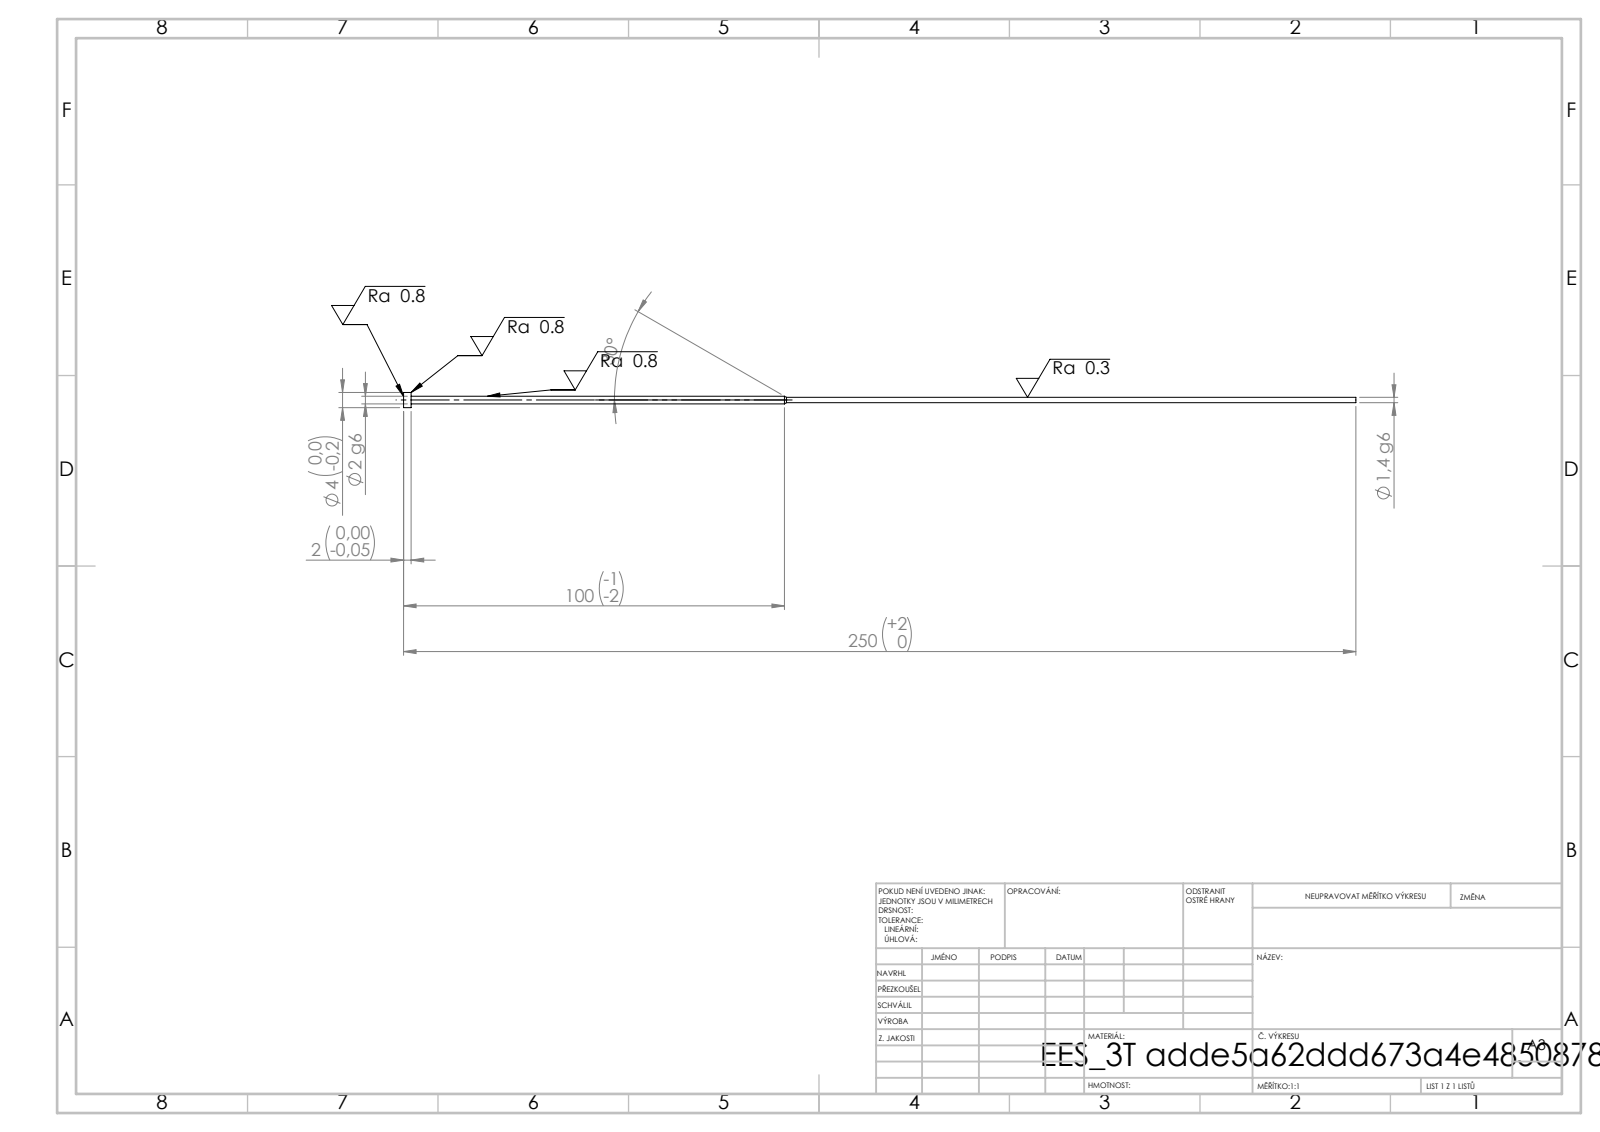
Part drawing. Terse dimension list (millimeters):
written by: SolidWorks 2019 (CONFIG_CONTROL_DESIGN)
unit: mm
bodies: 1 solid, 11 faces (3 planar, 6 cylindrical, 2 other)
size: 250 × 4 × 4
volume: 564 mm³; area: 1 325 mm²
bosses: 1× ⌀4, 1× ⌀2, 1× ⌀1.4
face distances: 2, 248, 250
